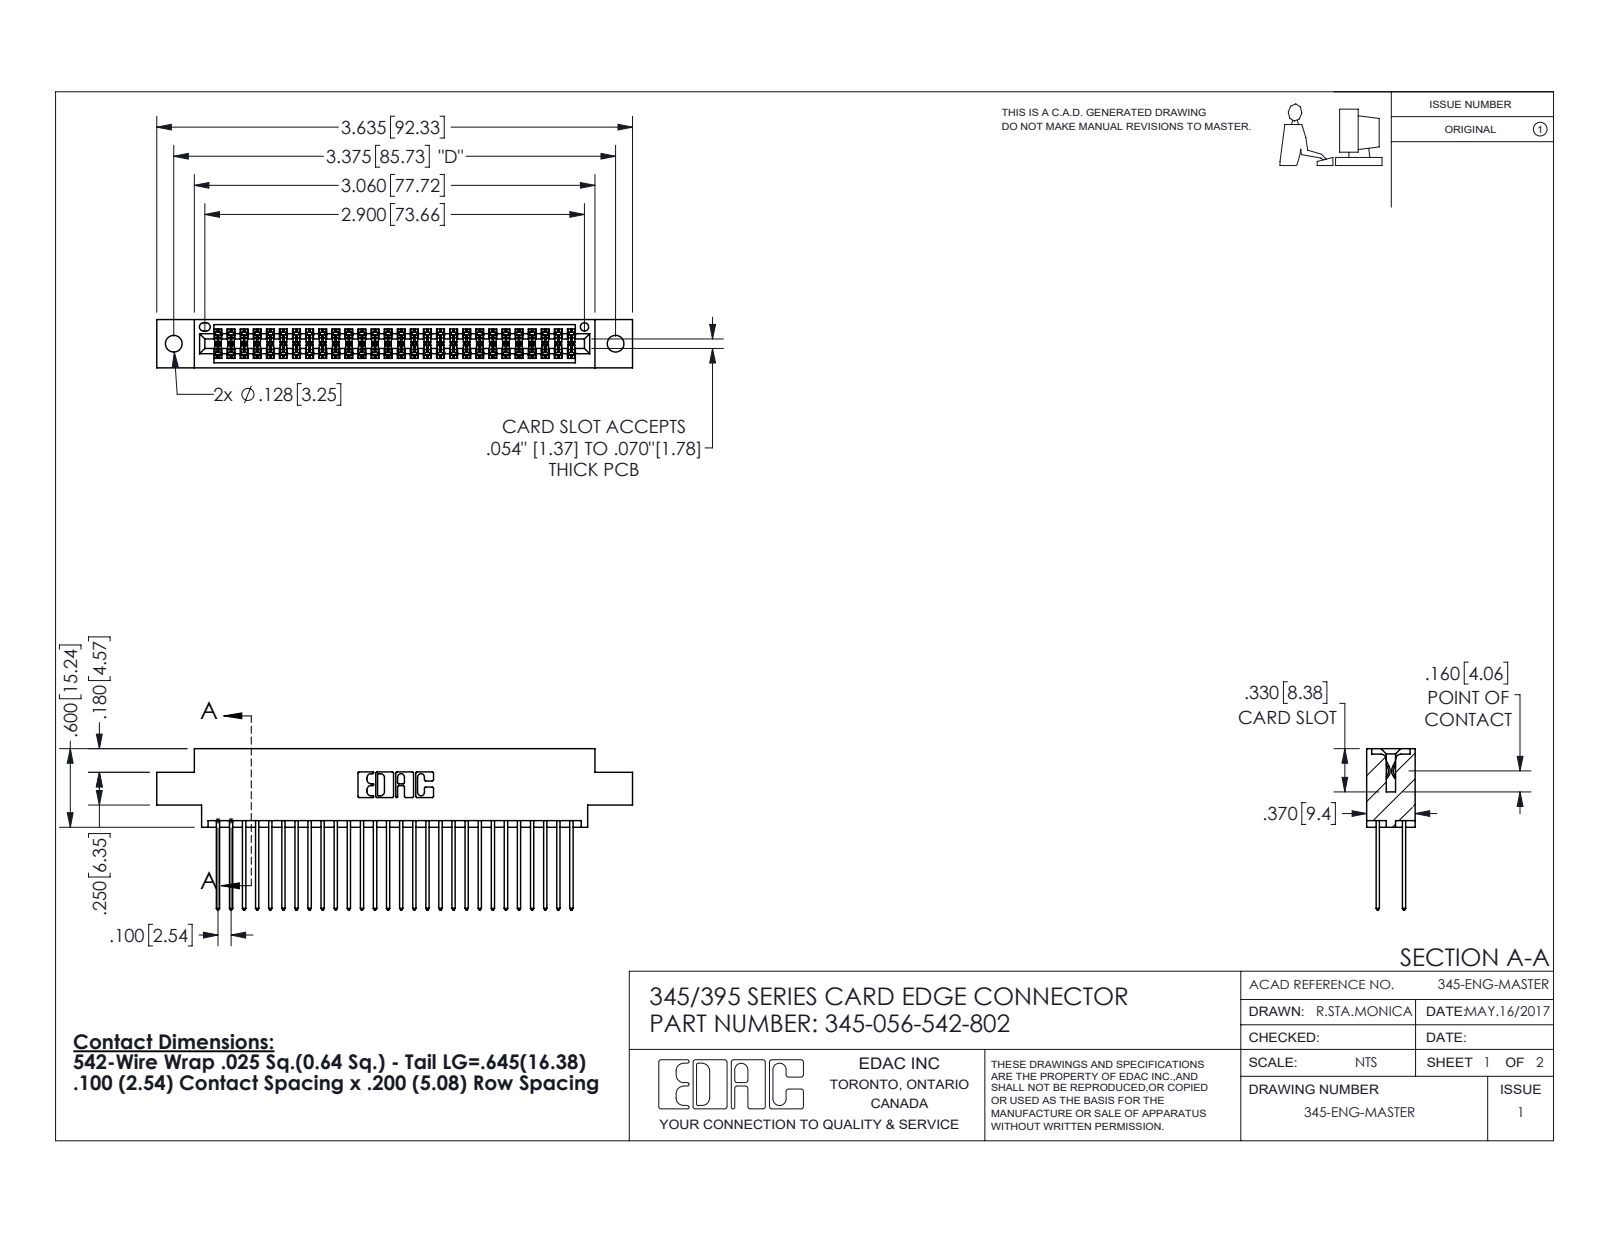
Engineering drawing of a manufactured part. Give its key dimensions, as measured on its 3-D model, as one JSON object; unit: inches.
{"part_name": "345-056-542-802; 345 Part_0.170 Offset - 0.128 Dia; 345-292-001_345-293-142", "step_written_by": "SolidWorks 2016 (CONFIG_CONTROL_DESIGN)", "units": "inches", "bodies": {"solids": 57, "faces": 2930, "planar": 1932, "cylindrical": 998, "other": 0}, "overall_size": [3.635, 1.232, 0.37], "volume_in3": 0.546, "surface_area_in2": 21.78, "round_holes": [[0.128, 2], [0.064, 1]], "partial_cylinders_radius": [[0.006, 84], [0.01, 56], [0.01, 22], [0.007, 6], [0.031, 6], [0.026, 3], [0.014, 2], [0.019, 2]], "face_to_face_distances": [0.298, 0.072, 0.2, 0.098, 0.272, 0.025, 0.37, 0.225, 0.175, 0.149], "hole_center_spacings": [0.27, 3.14, 3.375]}
